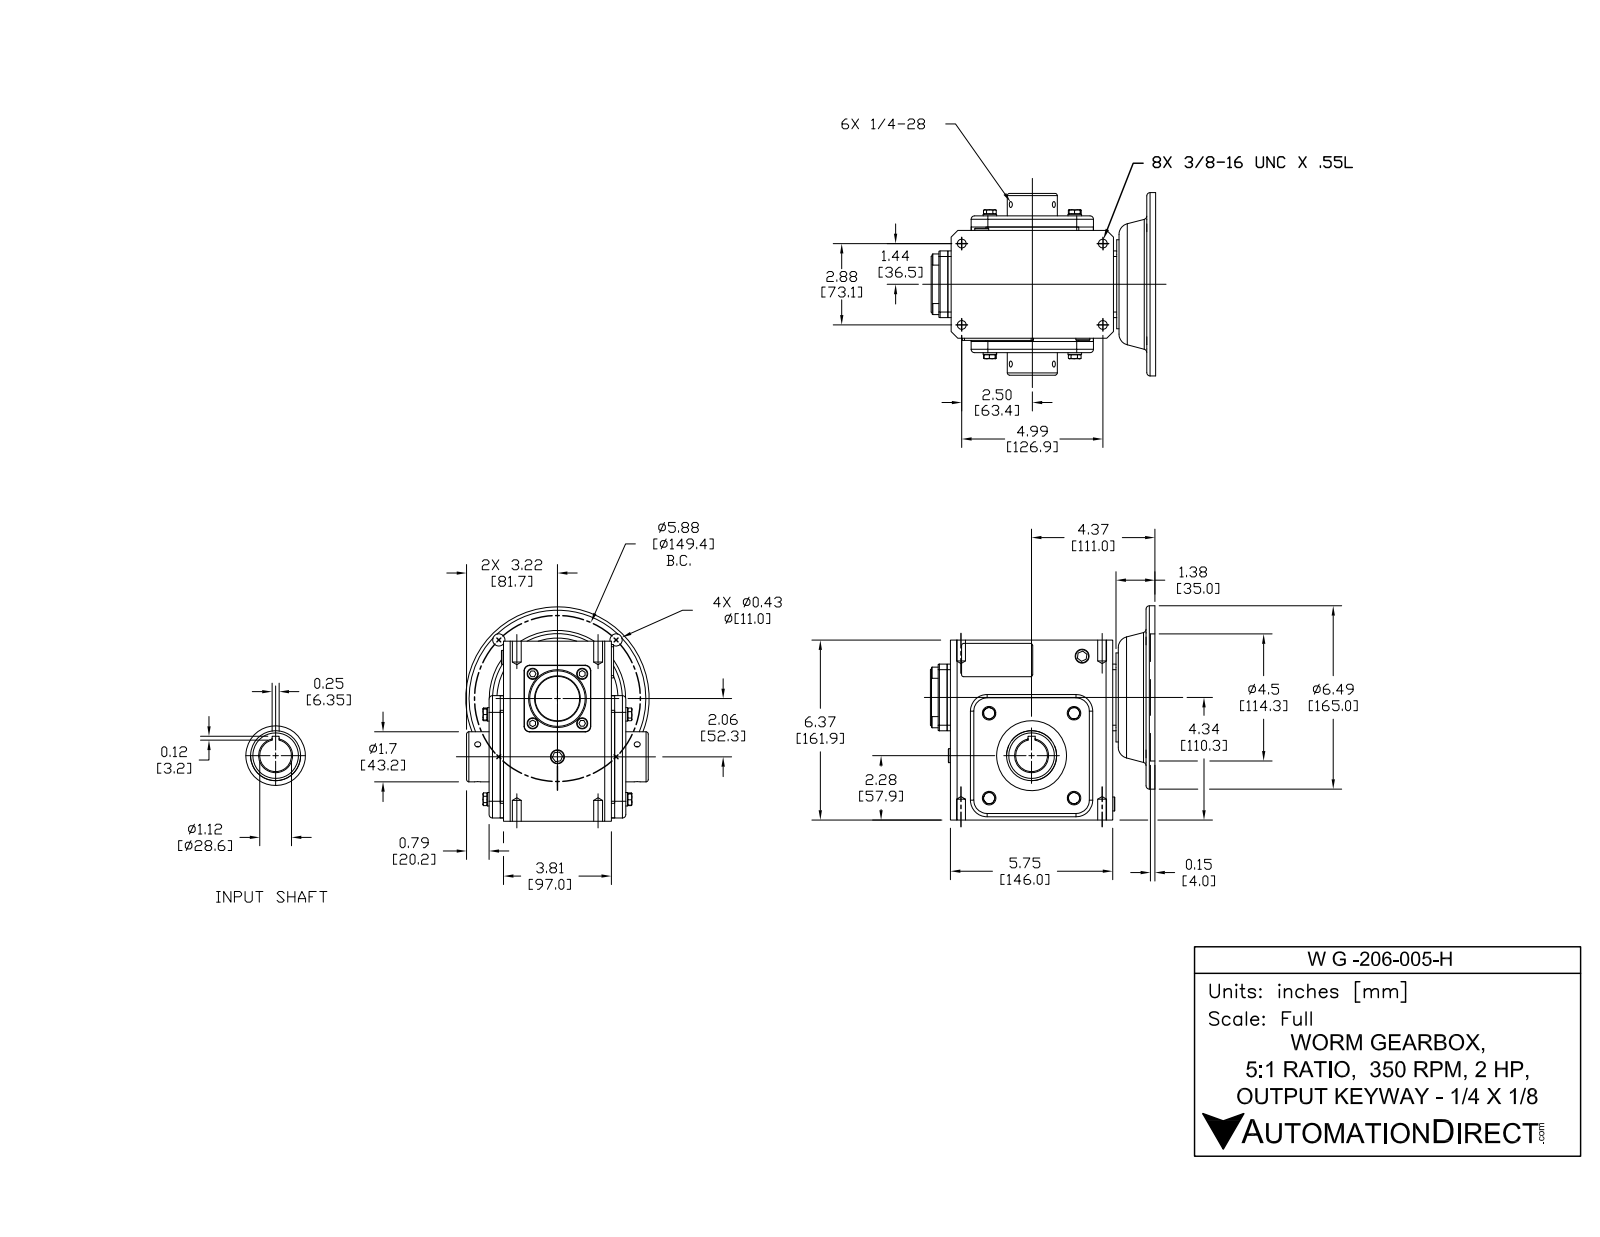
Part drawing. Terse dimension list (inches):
name: WG-206-005-H
written by: SolidWorks 2015 (CONFIG_CONTROL_DESIGN)
unit: in
bodies: 45 solids, 628 faces (304 planar, 198 cylindrical, 126 other)
size: 7.953 × 7.591 × 6.496
volume: 171 in³; area: 463.1 in²
holes: 6× ⌀0.213, 4× ⌀0.313, 4× ⌀0.406, 1× ⌀0.591, 1× ⌀0.625, 1× ⌀1.125, 1× ⌀1.457, 1× ⌀1.772, 1× ⌀2.402, 1× ⌀3.543, 1× ⌀4.5
bosses: 8× ⌀0.394, 4× ⌀0.48, 1× ⌀6.496, 1× ⌀3.15, 1× ⌀2.047, 1× ⌀1.575, 1× ⌀1.181, 1× ⌀1.142
rounds: 8× R0.079, 8× R0.118, 4× R0.197, 4× R0.591, 2× R0.02, 2× R0.039, 1× R2.717
face distances: 0.118, 4.055, 0.394, 4.331, 3.937, 0.512, 4.449, 6.375, 5.866, 1.181
hole spacings: 2.858, 2.937, 4.154, 4.943, 5.65, 2.077, 2.88, 4.631
